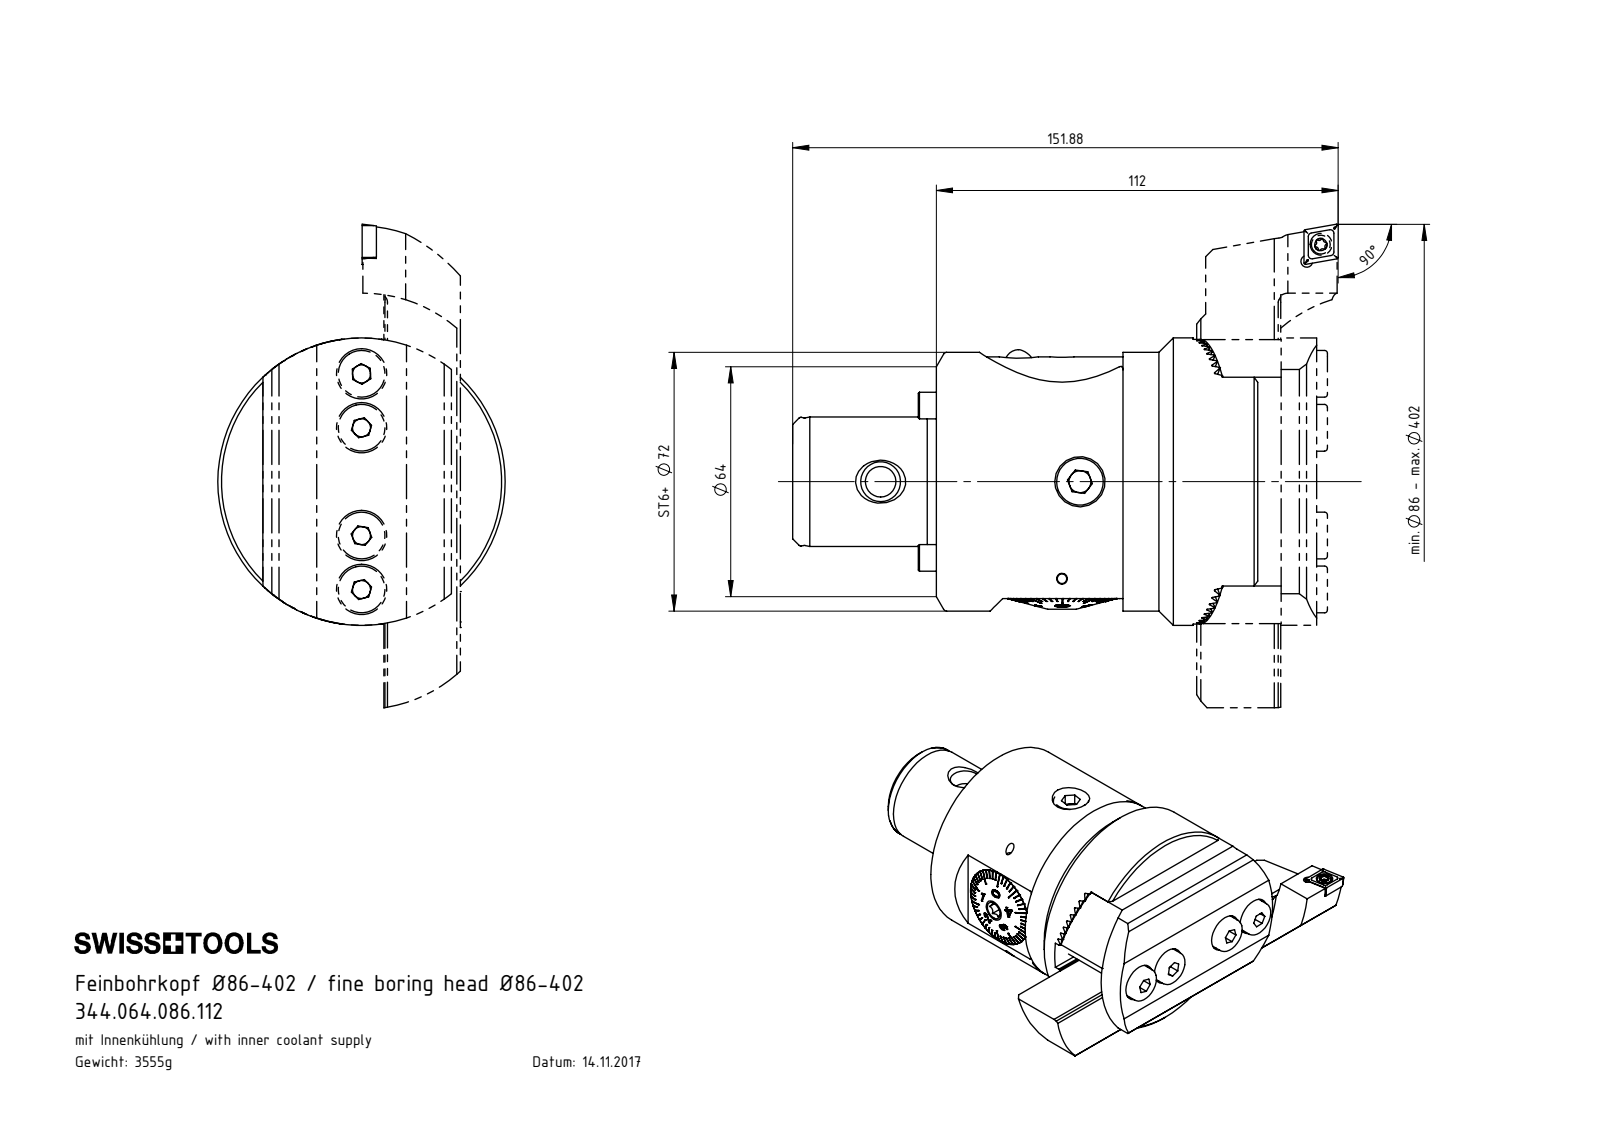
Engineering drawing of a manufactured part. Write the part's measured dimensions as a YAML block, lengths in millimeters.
part_name: "ISO 2338 - 3 h8 x 6; A55-BG2.001.000_B; ISO 4762 - M6 x 35; ST6-ER2.001.012_A (+8 more)"
step_written_by: "SolidWorks 2017 (CONFIG_CONTROL_DESIGN)"
units: millimeters
bodies: {solids: 26, faces: 1042, planar: 447, cylindrical: 239, other: 356}
overall_size: [148.88, 80, 80]
volume: 382847
surface_area: 102329
round_holes:
  - {diameter: 5, count: 7}
  - {diameter: 8.5, count: 5}
  - {diameter: 14, count: 5}
  - {diameter: 6.8, count: 4}
  - {diameter: 7, count: 4}
  - {diameter: 10, count: 4}
  - {diameter: 10.5, count: 4}
  - {diameter: 3, count: 2}
  - {diameter: 6, count: 2}
  - {diameter: 16, count: 2}
  - {diameter: 1, count: 1}
  - {diameter: 3.15, count: 1}
round_bosses_or_shafts:
  - {diameter: 8, count: 6}
  - {diameter: 13, count: 5}
  - {diameter: 10, count: 4}
  - {diameter: 6, count: 4}
  - {diameter: 80, count: 1}
  - {diameter: 72, count: 1}
  - {diameter: 36, count: 1}
  - {diameter: 35.8, count: 1}
partial_cylinders:
  - {radius: 0.2, count: 16}
  - {radius: 0.5, count: 4}
  - {radius: 5.47, count: 2}
  - {radius: 18.05, count: 2}
  - {radius: 40, count: 2}
  - {radius: 10.25, count: 1}
  - {radius: 23, count: 1}
  - {radius: 36, count: 1}
face_to_face_distances: [43.88, 2.38, 52, 4.76, 95.88, 7.14, 10, 105.88, 53.88, 7.15]
hole_center_spacings: [12, 12.04, 13.2, 15, 18.44, 20, 33.24, 34.18]
